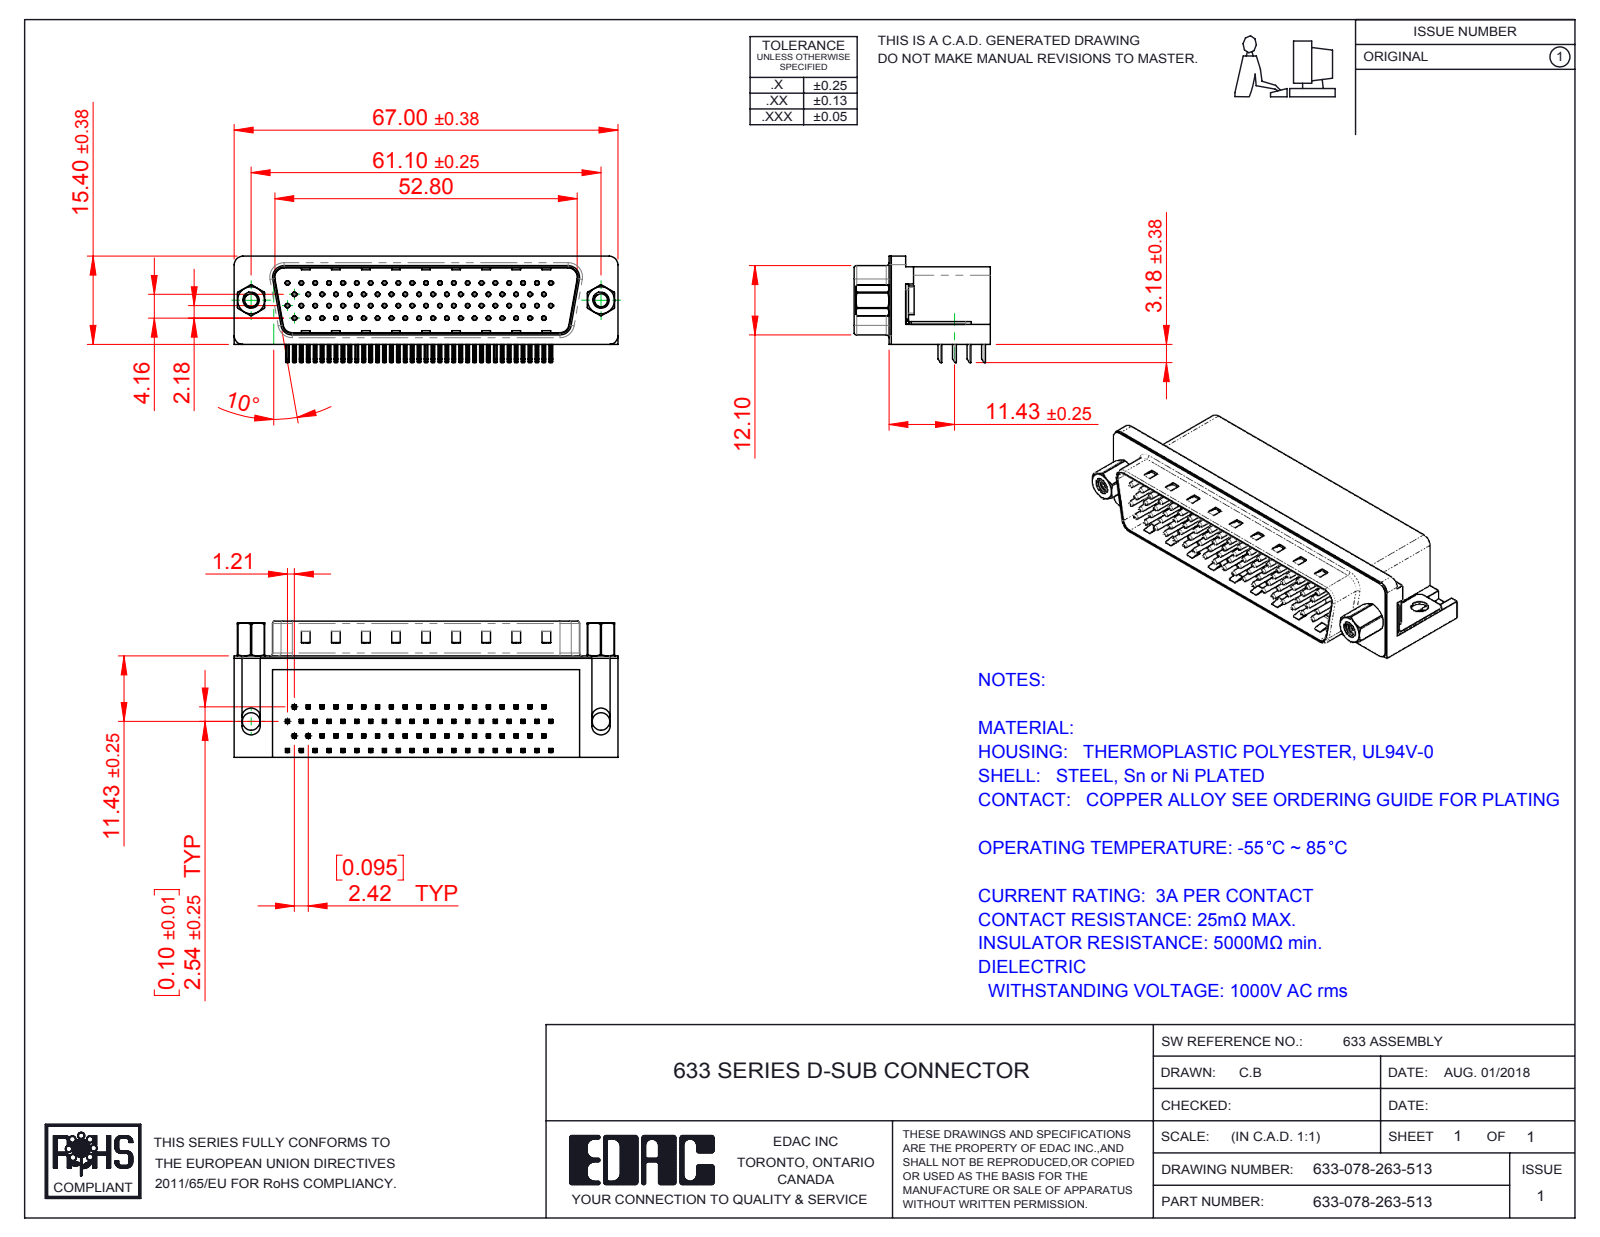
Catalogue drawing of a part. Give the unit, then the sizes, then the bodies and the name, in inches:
Units: inches
Overall size (bounding box): 2.638 × 0.937 × 0.731
Round holes (diameter × count): ⌀0.014 ×78, ⌀0.031 ×78, ⌀0.089 ×2, ⌀0.09 ×2, ⌀0.12 ×2, ⌀0.157 ×2, ⌀0.189 ×2, ⌀0.197 ×2
Round bosses / shafts (diameter × count): ⌀0.03 ×78, ⌀0.193 ×2, ⌀0.187 ×2, ⌀0.154 ×2, ⌀0.11 ×2
Partial cylindrical surfaces — rounded edges, fillets, slot ends (radius × count): R0.01 ×320, R0.005 ×156, R0.039 ×16, R0.02 ×9, R0.063 ×8, R0.059 ×6, R0.018 ×4, R0.035 ×4
Main face-to-face distances: 0.016, 0.52, 0.681, 0.461, 0.526, 0.081, 0.541, 0.065, 0.073, 0.469
Hole centre spacings: 0.095, 0.191, 0.286, 0.381, 0.246, 0.281, 0.476, 0.339
Volume: 0.904 in³ · Surface area: 26.02 in²
Bodies: 86 solids, 6394 faces (4001 planar, 1842 cylindrical, 551 other)
Part name (STEP PRODUCT): 633 4-40 Threaded Rivet; 633 Thru Hole Board Mount_78 Contact; 633 Contact Top 78; 633 Contact Top_78 Contact (+6 more)
STEP written by: SolidWorks 2016 (CONFIG_CONTROL_DESIGN)
